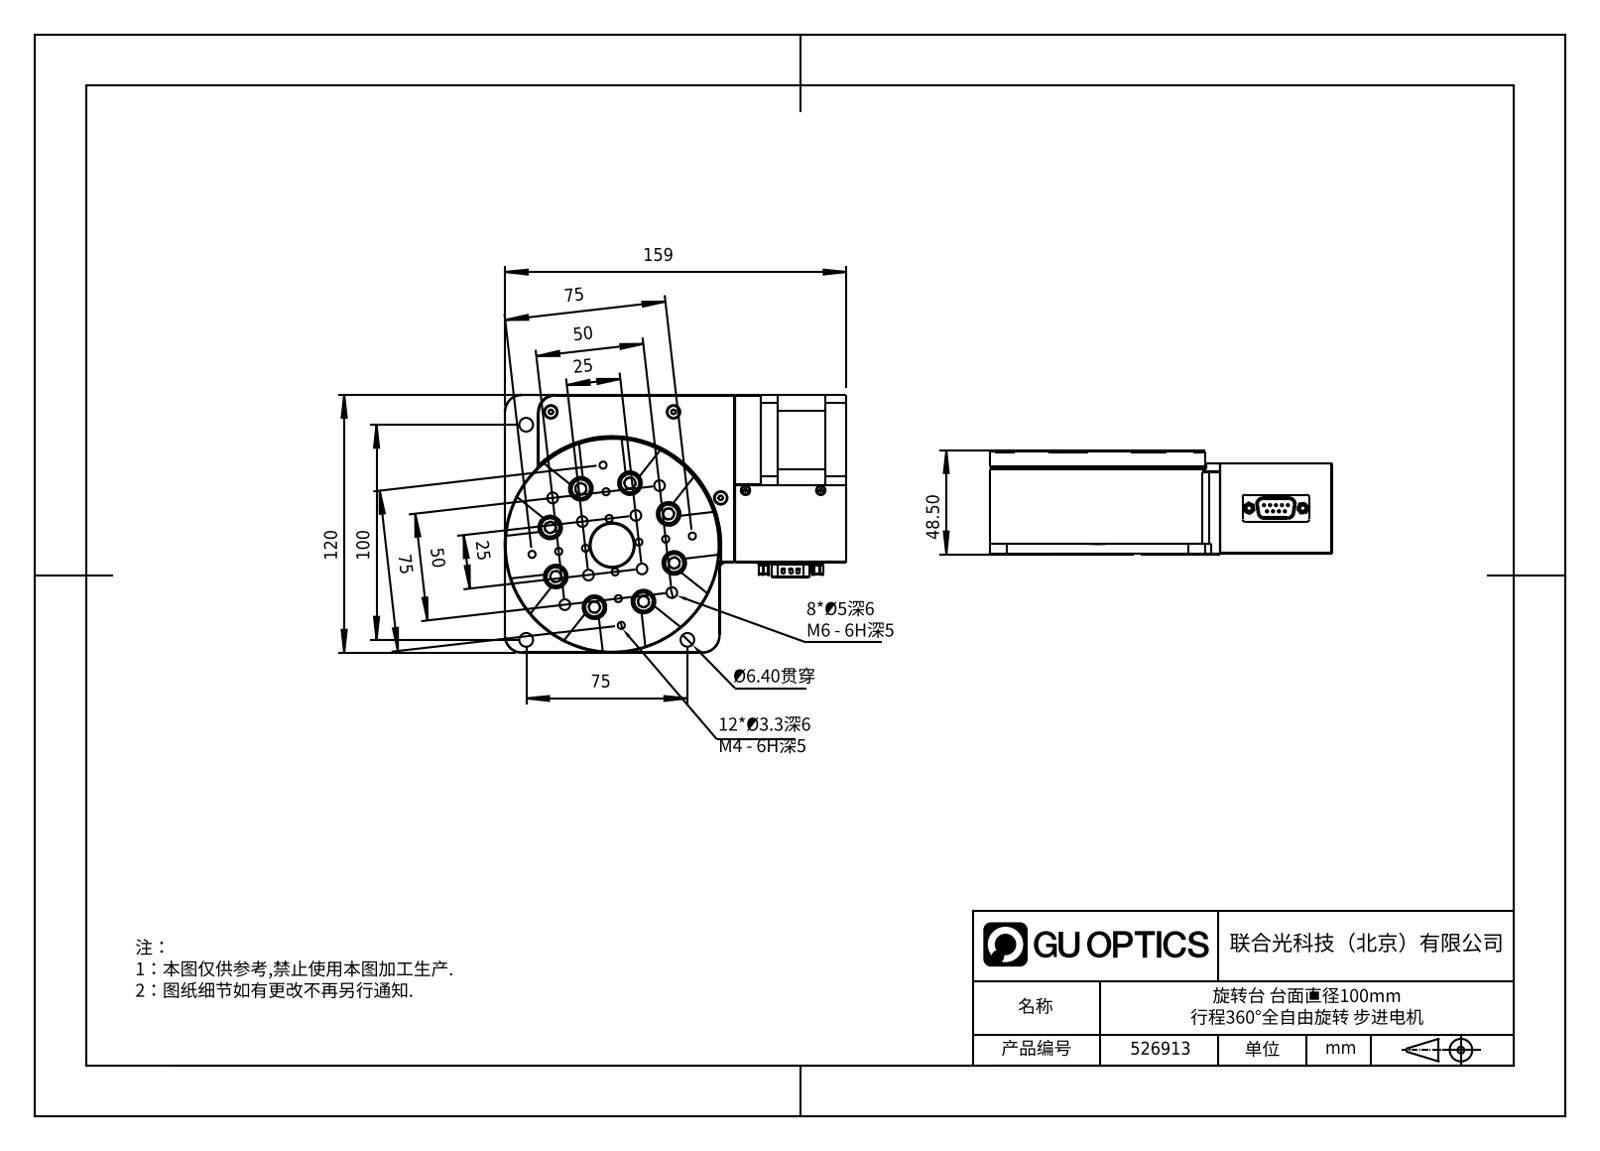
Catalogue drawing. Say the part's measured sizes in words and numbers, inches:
The part is named "FMSR100". Its 3-D file was written by "SolidWorks 2020 (CONFIG_CONTROL_DESIGN)". It is 107 solids with 3511 faces: 1615 planar, 1080 cylindrical and 816 other. Overall it measures 6.26 by 4.724 by 1.909 inches. Its volume is 29.18 cubic inches and its surface area 308 square inches. Round holes: 28 of diameter 0.098, 26 of diameter 0.134, 23 of diameter 0.13, 20 of diameter 0.256, 16 of diameter 0.197, 9 of diameter 0.043, 8 of diameter 0.177, 8 of diameter 0.26, 8 of diameter 0.315, 8 of diameter 0.433, 5 of diameter 0.118, 5 of diameter 0.236. Round bosses or shafts: 24 of diameter 0.118, 23 of diameter 0.217, 11 of diameter 0.276, 11 of diameter 0.157, 9 of diameter 0.236, 9 of diameter 0.059, 9 of diameter 0.039, 8 of diameter 0.394. Partial cylindrical surfaces (rounded edges, fillets, slot ends): 39 of radius 0.02, 19 of radius 0.039, 16 of radius 0.118, 12 of radius 0.012, 11 of radius 0.079, 8 of radius 0.016, 6 of radius 0.197, 6 of radius 0.315. The main face-to-face distances are 0.02, 0.236, 0.039, 0.571, 0.394, 1.319, 0.669, 1.654, 0.335, 0.177. The hole center spacings are 0.551, 0.124, 1.122, 0.109, 1.181, 0.218, 1.096, 1.213.
